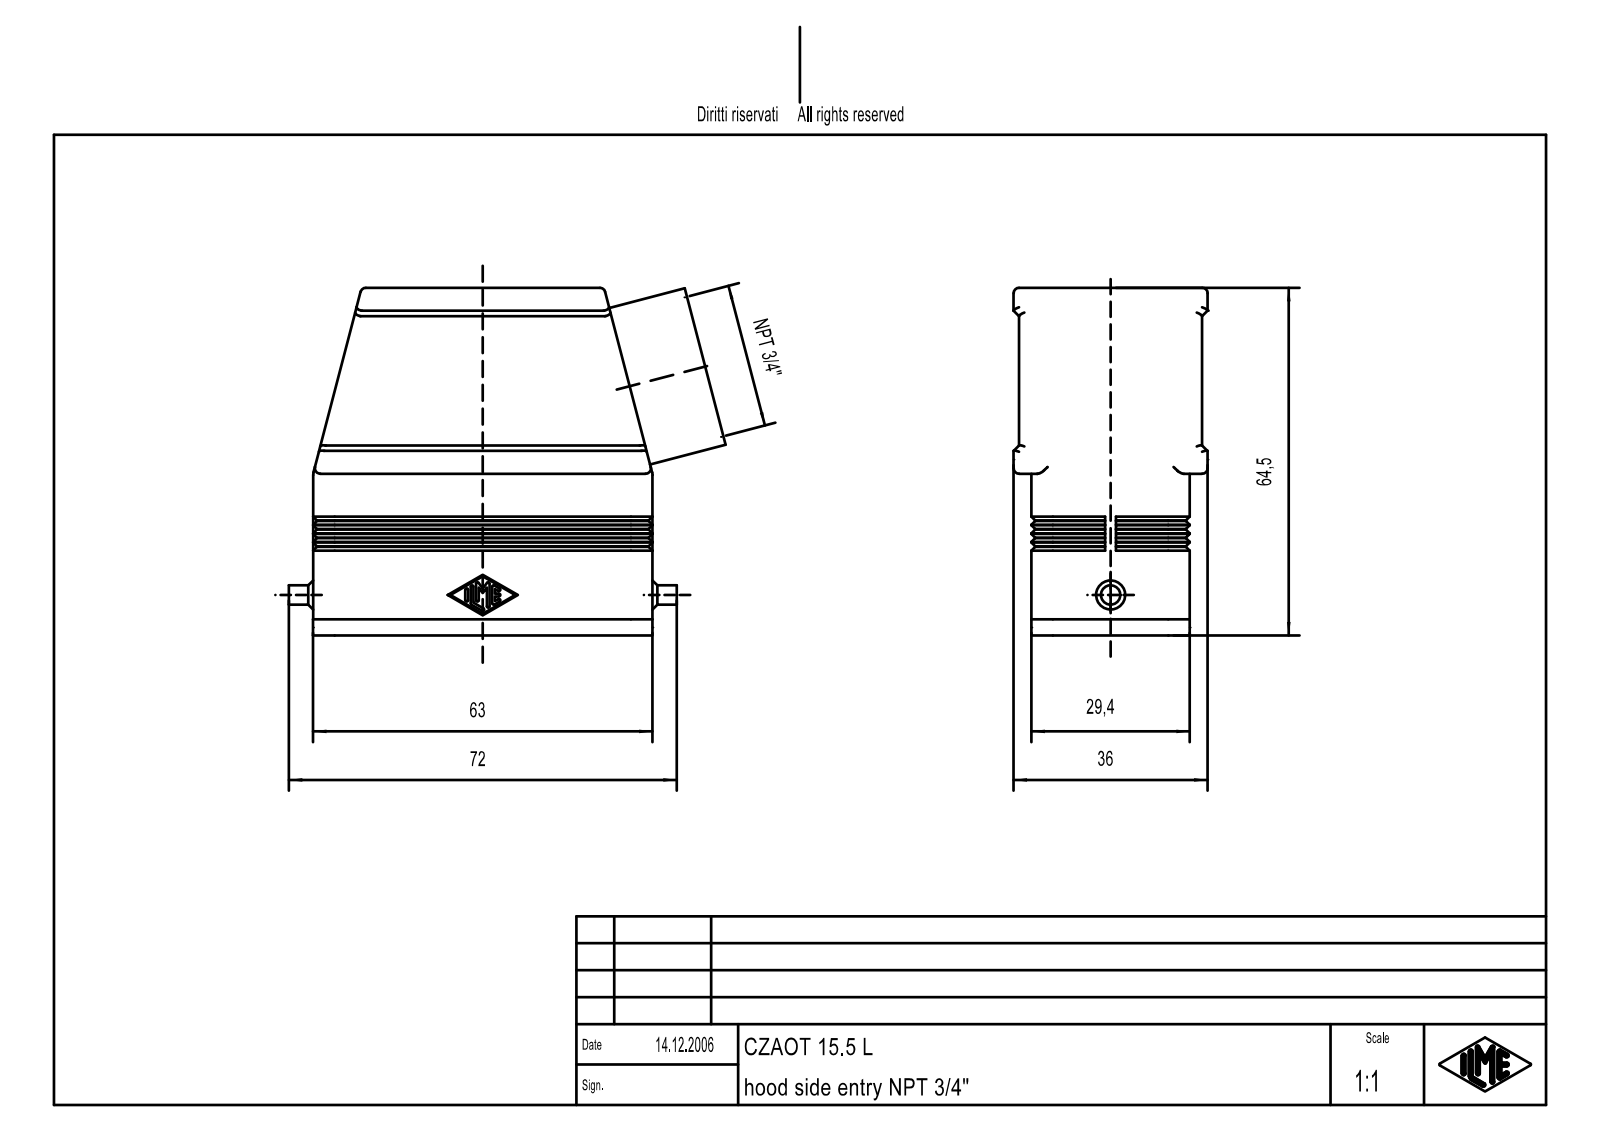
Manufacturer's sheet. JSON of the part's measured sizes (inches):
{"part_name": "CZ_MZ_T\\S\\|llengeh\\S\\duse_1_B\\S\\|gel", "step_written_by": "Creo Elements/Direct Modeling 18.0B 02-Dec-2011 (C) Parametric Technology GmbH (AUTOMOTIVE_DESIGN)", "units": "inches", "bodies": {"solids": 0, "faces": 375, "planar": 193, "cylindrical": 124, "other": 58}, "overall_size": [3.192, 2.539, 1.417], "round_holes": [[0.097, 4], [0.138, 4]], "round_bosses_or_shafts": [[1.181, 1], [0.142, 1]], "partial_cylinders_radius": [[0.039, 24], [0.01, 14], [0.157, 8], [0.079, 6], [0.049, 4], [0.13, 4], [0.591, 1]], "face_to_face_distances": [0.118, 1.13, 0.209, 0.921, 0.091, 1.248, 1.039, 1.339, 1.157, 0.394], "hole_center_spacings": [0.63, 1.949, 2.048]}
